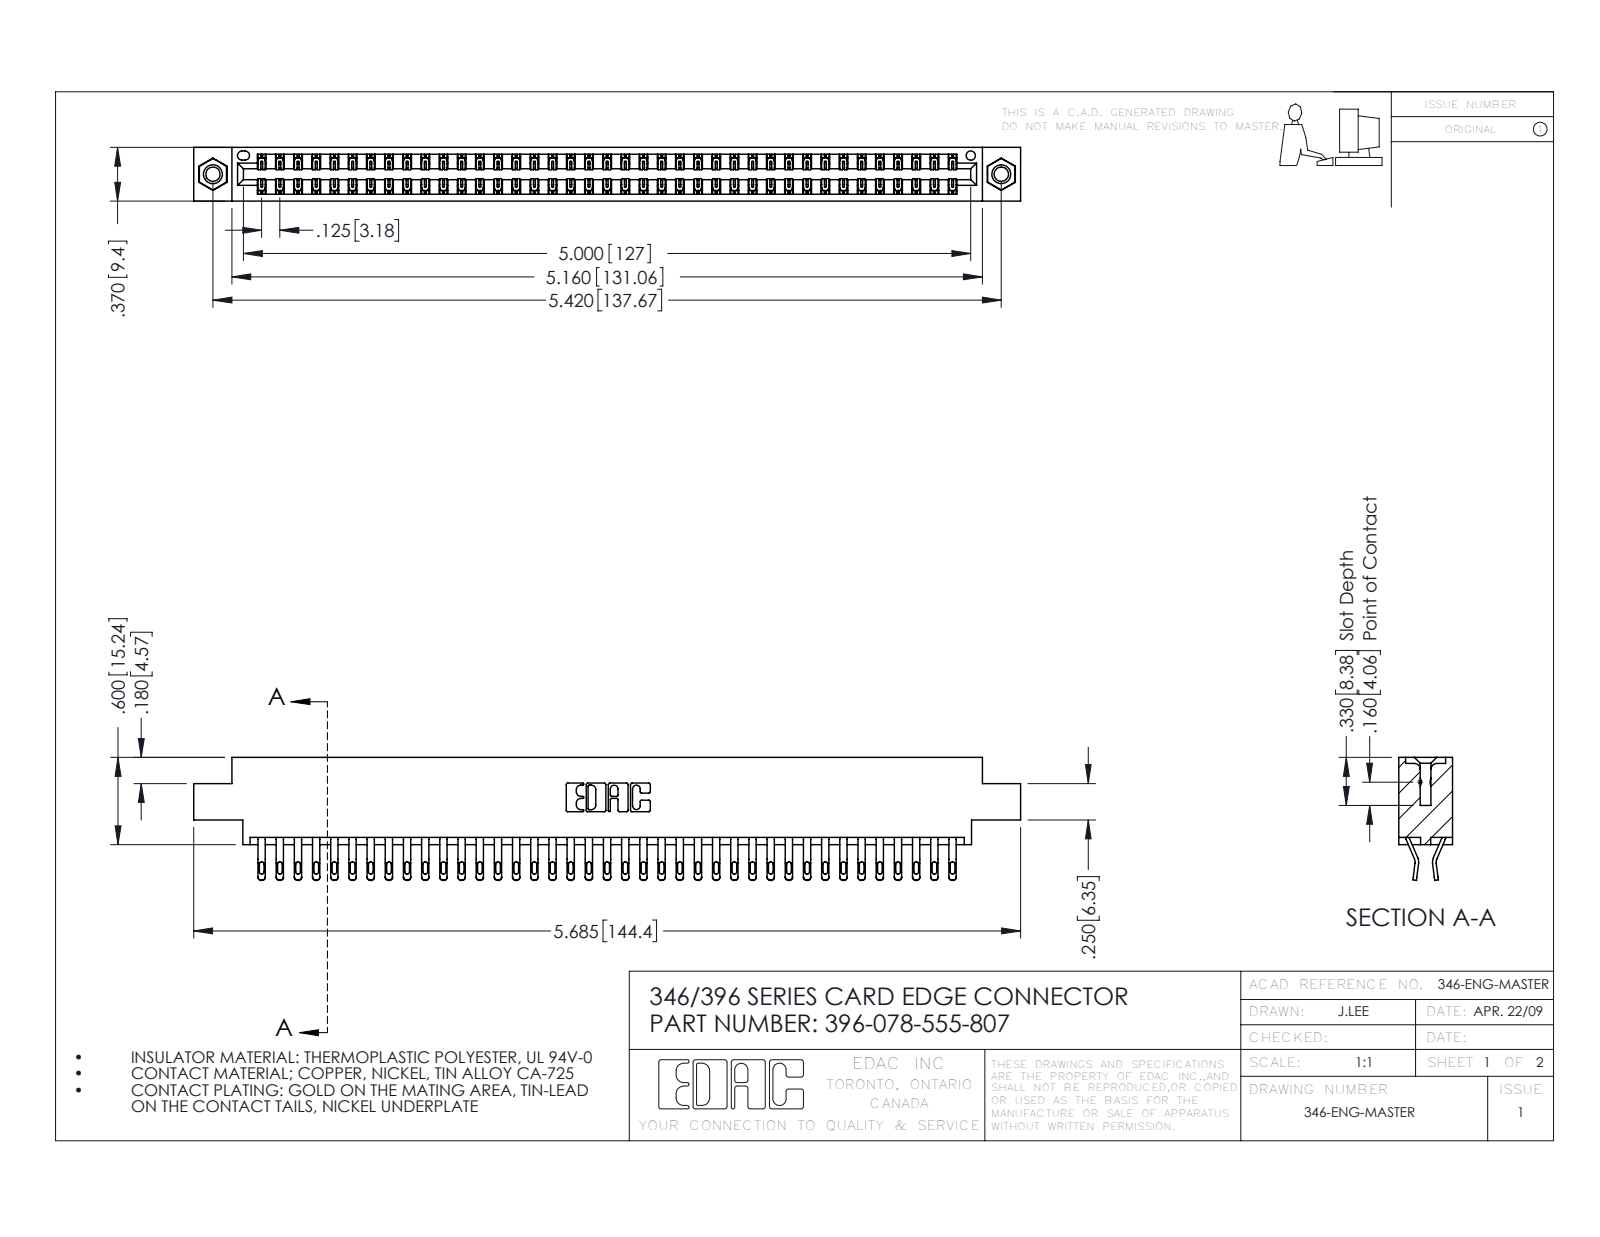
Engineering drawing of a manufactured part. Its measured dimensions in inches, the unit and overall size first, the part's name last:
Units: inches
Overall size (bounding box): 5.685 × 0.845 × 0.37
Round holes (diameter × count): ⌀0.098 ×2, ⌀0.125 ×2, ⌀0.156 ×2, ⌀0.064 ×1
Round bosses / shafts (diameter × count): ⌀0.155 ×2
Partial cylindrical surfaces — rounded edges, fillets, slot ends (radius × count): R0.016 ×156, R0.02 ×156, R0.006 ×117, R0.01 ×22, R0.007 ×6, R0.031 ×6, R0.026 ×3, R0.01 ×2
Main face-to-face distances: 0.048, 0.322, 0.37, 0.25, 0.025, 0.072, 0.298, 0.275, 0.222, 0.148
Hole centre spacings: 0.246, 5.211, 5.42
Volume: 0.861 in³ · Surface area: 31.58 in²
Bodies: 81 solids, 4710 faces (2686 planar, 2008 cylindrical, 16 other)
Part name (STEP PRODUCT): 396-078-555-807; 345-292-001_555 Tail; 345-250-001_345-250-005-103; 346 Part_0.170 Offset - 0.156 Dia-TI
STEP written by: SolidWorks 2016 (CONFIG_CONTROL_DESIGN)
